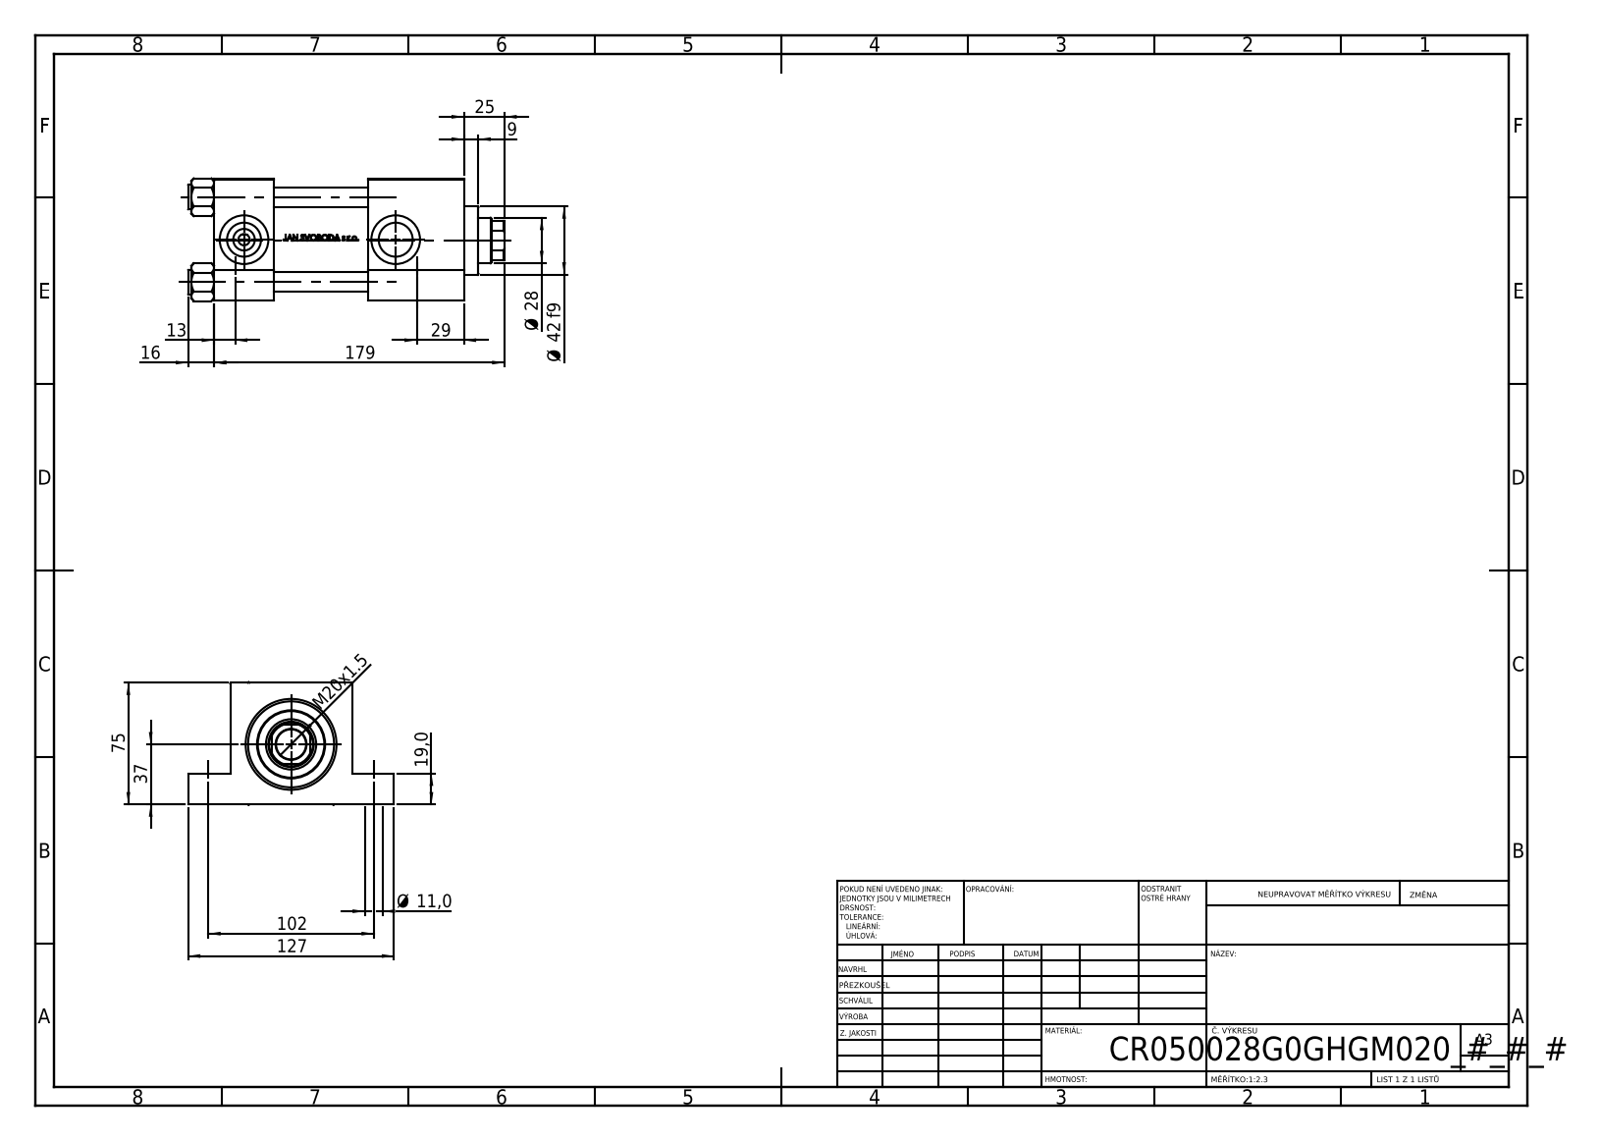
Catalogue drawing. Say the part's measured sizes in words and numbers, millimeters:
The part is named "V215CR_VCP_G; V215CR_G_Body; V215CR_G_TYCINKA; NUT_M5_G (+1 more)". Its 3-D file was written by "SolidWorks 2019 (CONFIG_CONTROL_DESIGN)". It is 11 solids with 1087 faces: 431 planar, 124 cylindrical and 532 other. Overall it measures 195 by 127 by 75.54 millimeters. Its volume is 767 970 cubic millimeters and its surface area 162 970 square millimeters. Round holes: 4 of diameter 12, 3 of diameter 11, 2 of diameter 7, 2 of diameter 20.96, 2 of diameter 30, 1 of diameter 11, 1 of diameter 18.5, 1 of diameter 28, 1 of diameter 31, 1 of diameter 41, 1 of diameter 50, 1 of diameter 53. Round bosses or shafts: 4 of diameter 15, 1 of diameter 56, 1 of diameter 42. Partial cylindrical surfaces (rounded edges, fillets, slot ends): 1 of radius 13.5. The main face-to-face distances are 75, 37, 154, 117, 19, 56, 95, 58, 59, 26. The hole center spacings are 52.3, 36.63, 37.34, 73.96, 102, 112, 151.49, 93.5.
